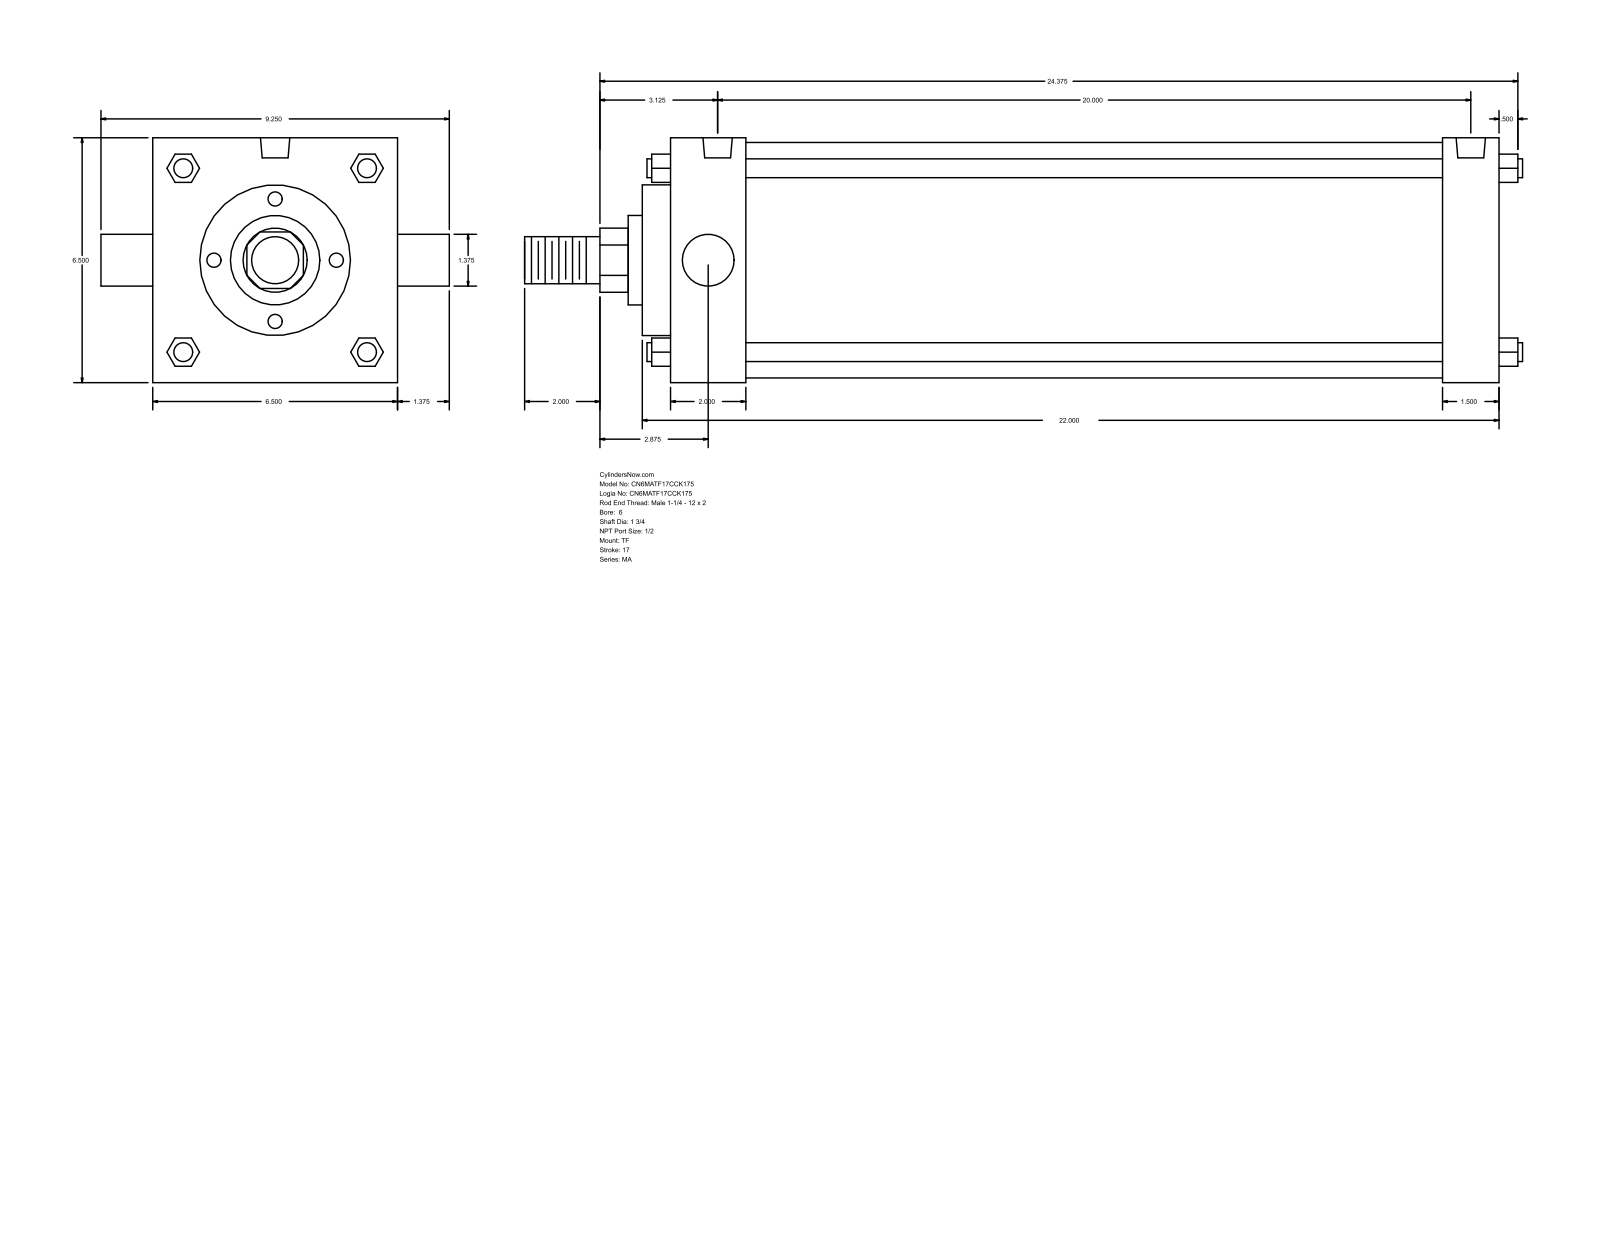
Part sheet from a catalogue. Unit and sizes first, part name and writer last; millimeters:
Units: millimetres
Overall size (bounding box): 673.1 × 234.95 × 165.1
Round holes (diameter × count): ⌀17.46 ×3, ⌀19.77 ×2
Round bosses / shafts (diameter × count): ⌀12.7 ×4, ⌀158.75 ×1, ⌀101.6 ×1, ⌀60.33 ×1, ⌀44.45 ×1, ⌀34.92 ×1, ⌀31.75 ×1
Partial cylindrical surfaces — rounded edges, fillets, slot ends (radius × count): R21.63 ×1
Main face-to-face distances: 165.1, 558.8, 19.05, 50.8, 508, 520.71, 469.91, 38.09, 69.85, 539.76
Hole centre spacings: 508
Bodies: 0 solids, 122 faces (93 planar, 29 cylindrical, 0 other)
Part name (STEP PRODUCT): MA_TF__0600_1.75
STEP written by: GSSL Pune (CONFIG_CONTROL_DESIGN)
